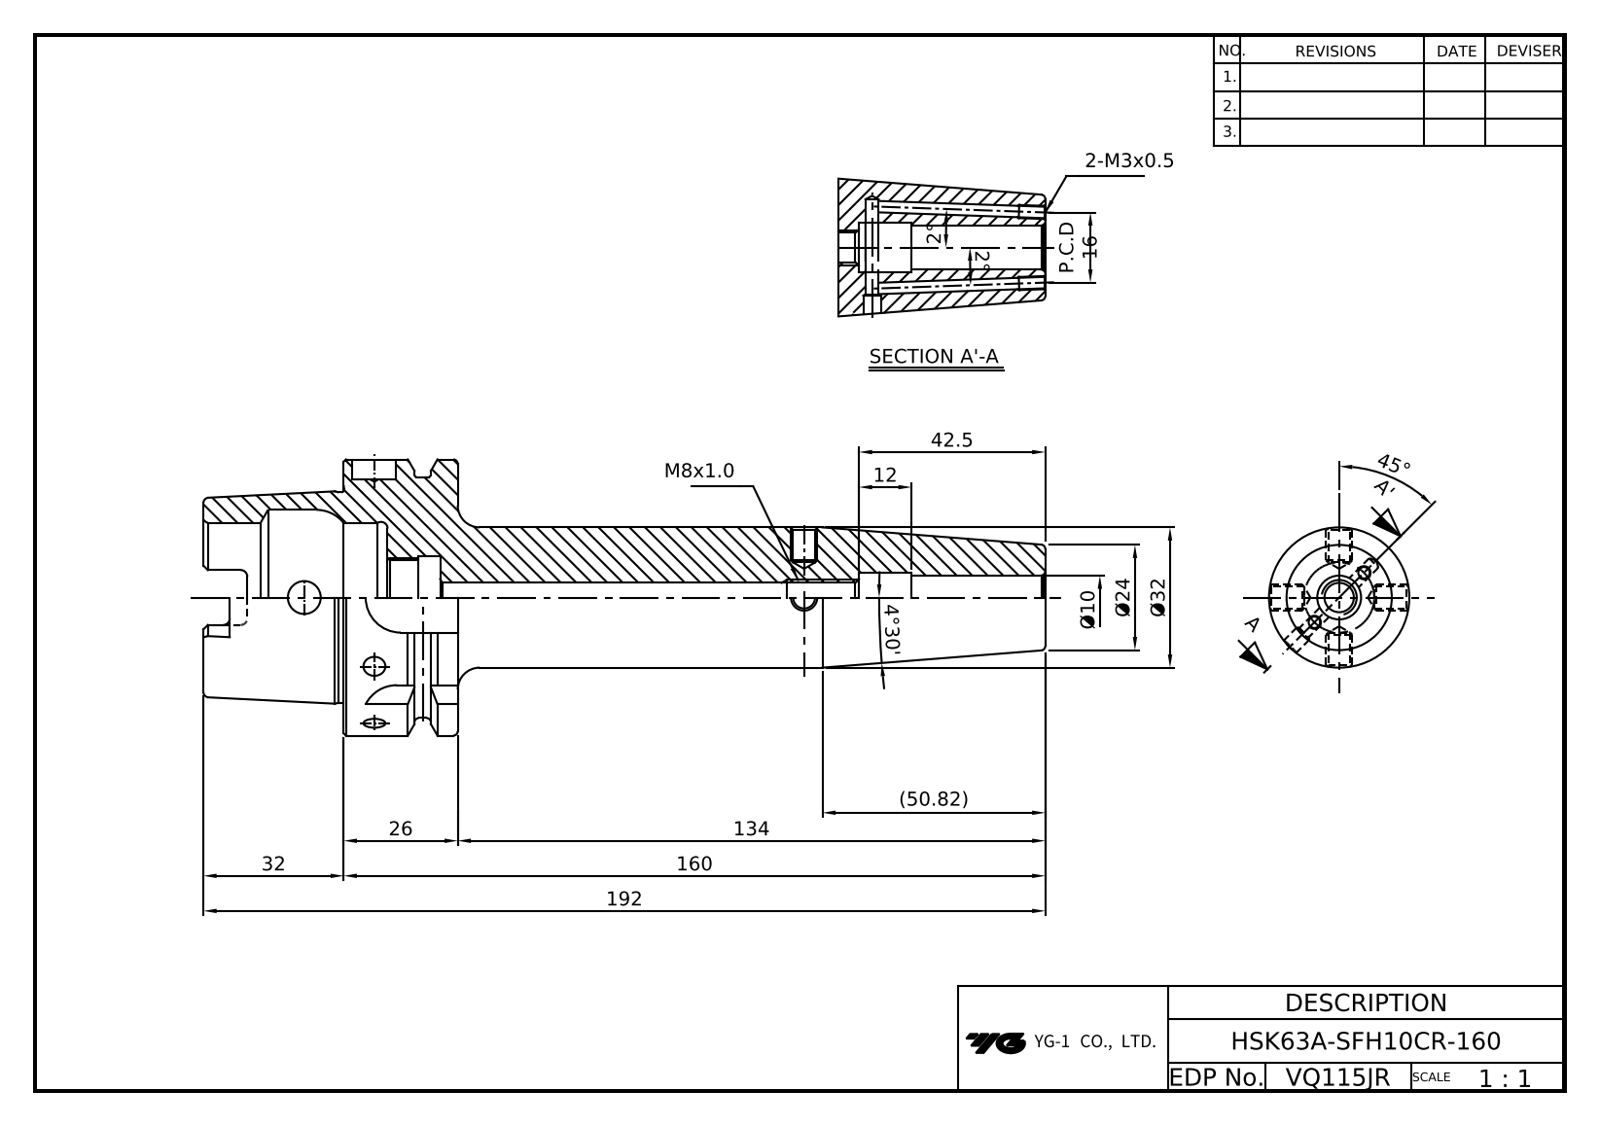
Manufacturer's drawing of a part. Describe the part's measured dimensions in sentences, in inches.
The part is named "LO-HSK63A-SFH10CR-160". Its 3-D file was written by "Autodesk Inventor 2022 (AUTOMOTIVE_DESIGN)". It is 1 solid with 119 faces: 42 planar, 35 cylindrical and 42 other. Overall it measures 7.559 by 2.48 by 2.48 inches. Its volume is 10.56 cubic inches and its surface area 59.77 square inches. Round holes: 2 of diameter 0.097, 2 of diameter 0.394, 1 of diameter 0.272, 1 of diameter 0.295, 1 of diameter 0.441, 1 of diameter 0.666, 1 of diameter 0.748, 1 of diameter 1.339, 1 of diameter 1.575. Round bosses or shafts: 1 of diameter 2.48, 1 of diameter 2.165, 1 of diameter 1.891, 1 of diameter 1.26. Partial cylindrical surfaces (rounded edges, fillets, slot ends): 6 of radius 0.059, 4 of radius 0.113, 4 of radius 0.315. The main face-to-face distances are 1.024, 0.394, 0.63, 1.26, 1.654, 2.283, 0.866, 0.157, 0.472, 2.087.
